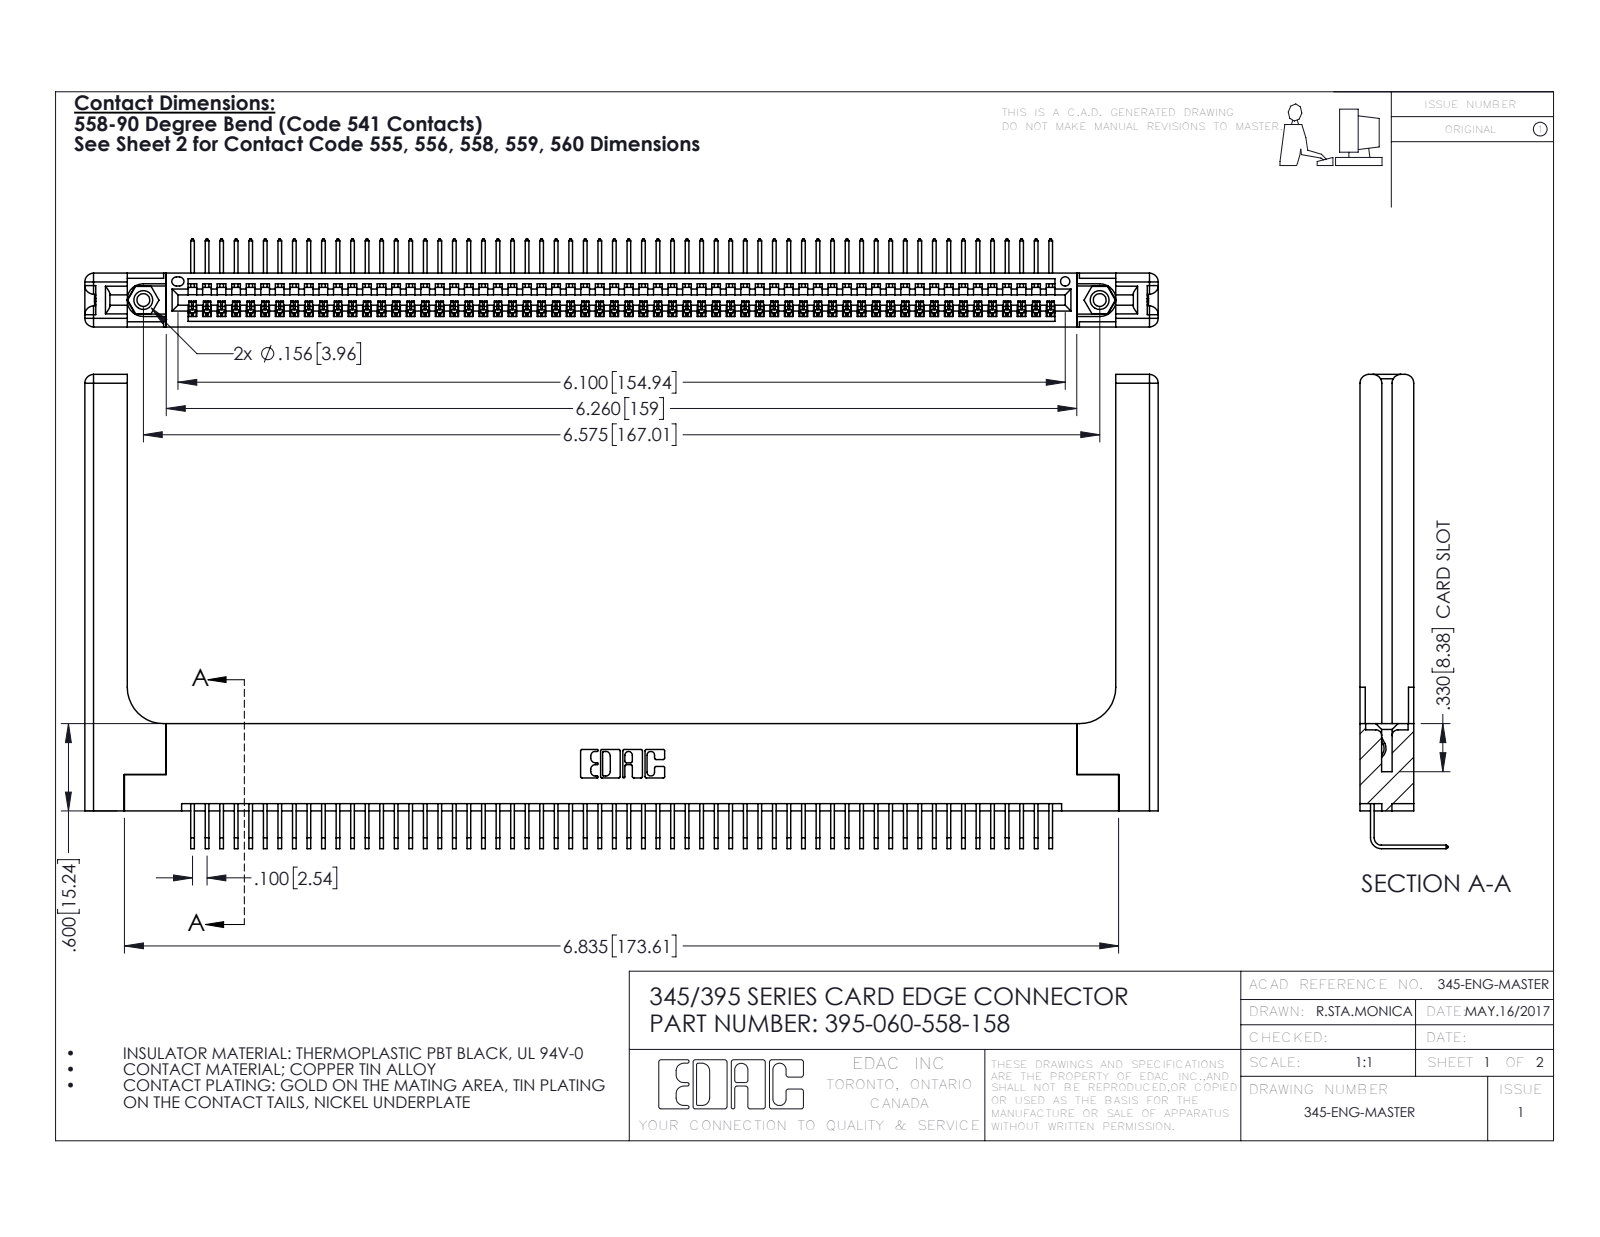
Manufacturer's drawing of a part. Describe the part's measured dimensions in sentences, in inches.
The part is named "345-220-058_345-220-058; 345 Part_Flush Mounting Lugs - 0.156 Dia-TH; 395-060-558-158; 345-292-001_558 Tail - 2 (+1 more)". Its 3-D file was written by "SolidWorks 2016 (CONFIG_CONTROL_DESIGN)". It is 65 solids with 3982 faces: 2748 planar, 1174 cylindrical and 60 other. Overall it measures 7.379 by 3.259 by 0.605 inches. Its volume is 1.627 cubic inches and its surface area 47.81 square inches. Round holes: 2 of diameter 0.089, 2 of diameter 0.125, 2 of diameter 0.156, 1 of diameter 0.064. Round bosses or shafts: 2 of diameter 0.155. Partial cylindrical surfaces (rounded edges, fillets, slot ends): 120 of radius 0.006, 22 of radius 0.01, 16 of radius 0.06, 6 of radius 0.007, 6 of radius 0.031, 3 of radius 0.026, 2 of radius 0.03, 2 of radius 0.031. The main face-to-face distances are 0.072, 0.37, 0.298, 0.2, 0.098, 0.272, 0.025, 0.225, 0.148, 0.15. The hole center spacings are 0.27, 6.339, 6.575.
